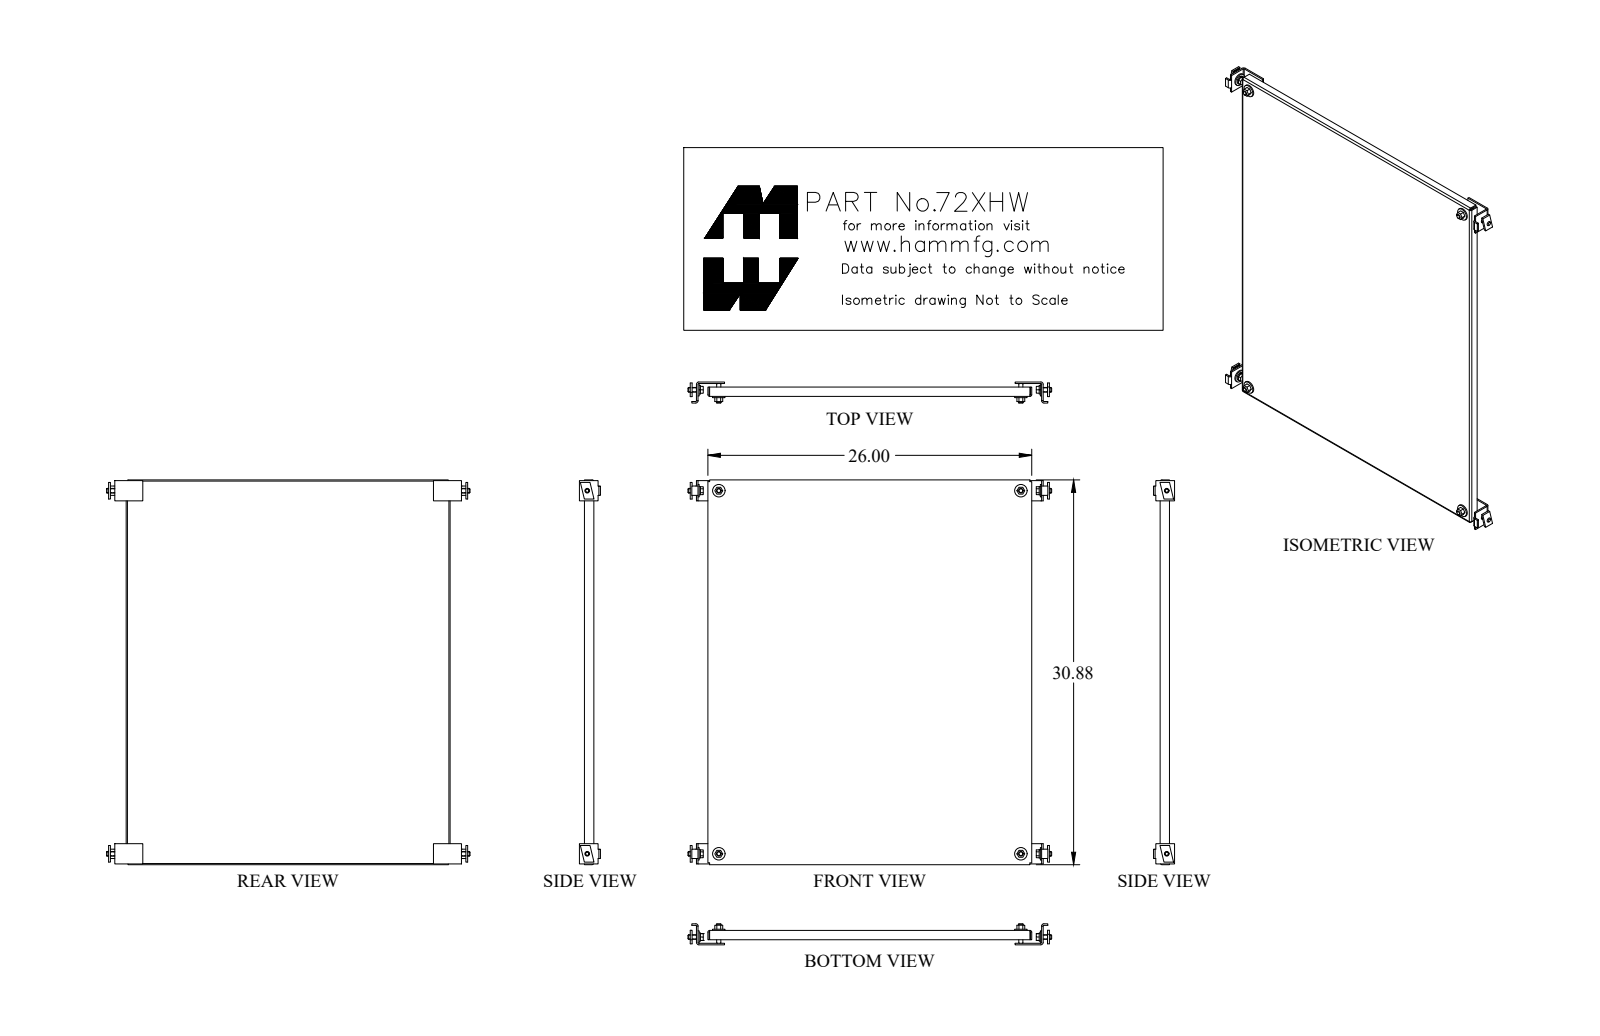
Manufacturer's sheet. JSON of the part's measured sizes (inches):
{"part_name": "72XHW_Default", "step_written_by": "SolidWorks 2018 (CONFIG_CONTROL_DESIGN)", "units": "inches", "bodies": {"solids": 1, "faces": 38, "planar": 22, "cylindrical": 16, "other": 0}, "overall_size": [30.875, 26, 0.75], "volume_in3": 82.73, "surface_area_in2": 1754, "round_holes": [[0.563, 4]], "partial_cylinders_radius": [[0.048, 4], [0.143, 4]], "face_to_face_distances": [0.095, 25.905, 30.78, 25.81, 26, 30.875, 30.685, 0.75, 0.655, 0.143], "hole_center_spacings": [24.25, 29.125, 37.899]}
